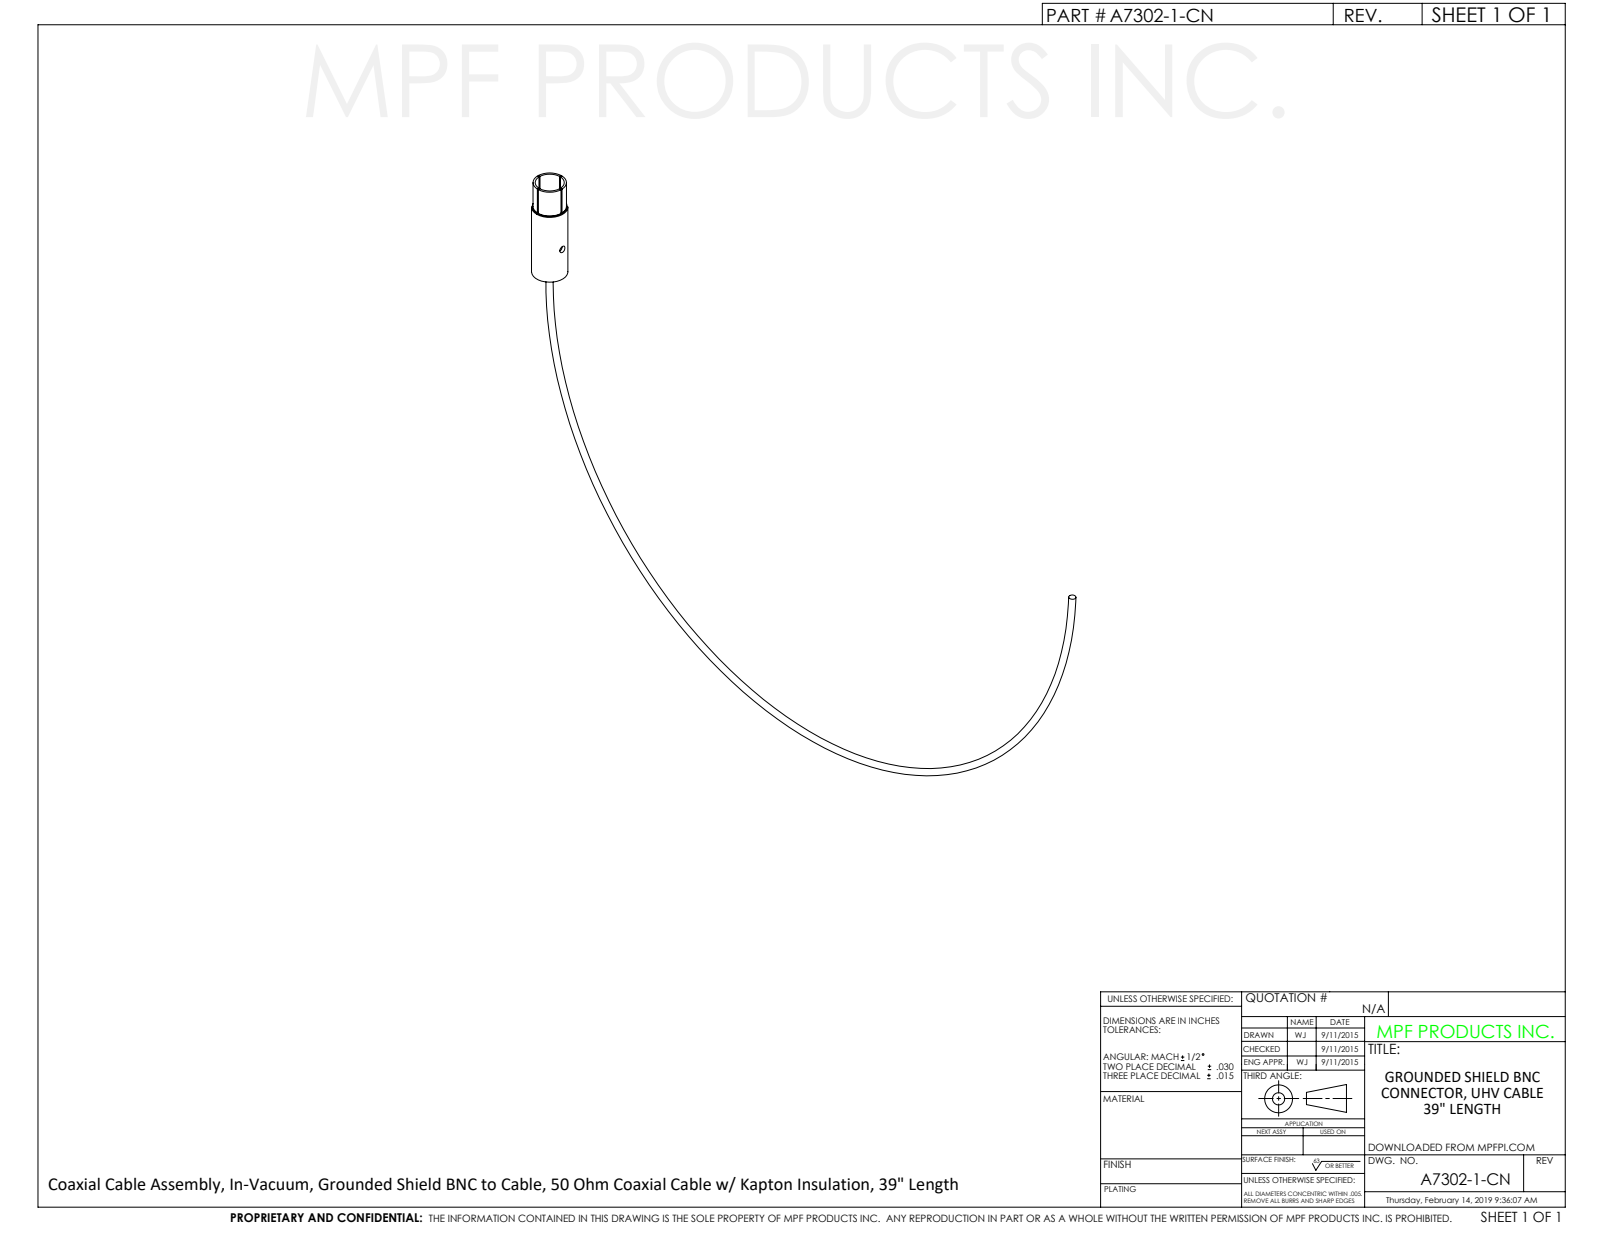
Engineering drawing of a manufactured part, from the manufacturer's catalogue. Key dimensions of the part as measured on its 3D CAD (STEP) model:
Part name (STEP PRODUCT): A7302-1-CN
STEP written by: SolidWorks 2012 (CONFIG_CONTROL_DESIGN)
Units: inches
Bodies: 1 solid, 34 faces (17 planar, 12 cylindrical, 5 other)
Overall size (bounding box): 10.587 × 6.833 × 0.75
Volume: 0.509 in³ · Surface area: 11.78 in²
Round holes (diameter × count): ⌀0.1 ×2, ⌀0.5 ×1
Round bosses / shafts (diameter × count): ⌀0.75 ×1, ⌀0.71 ×1
Main face-to-face distances: 1.5, 0.2, 1.3, 0.02, 1.1, 0.9, 0.4
